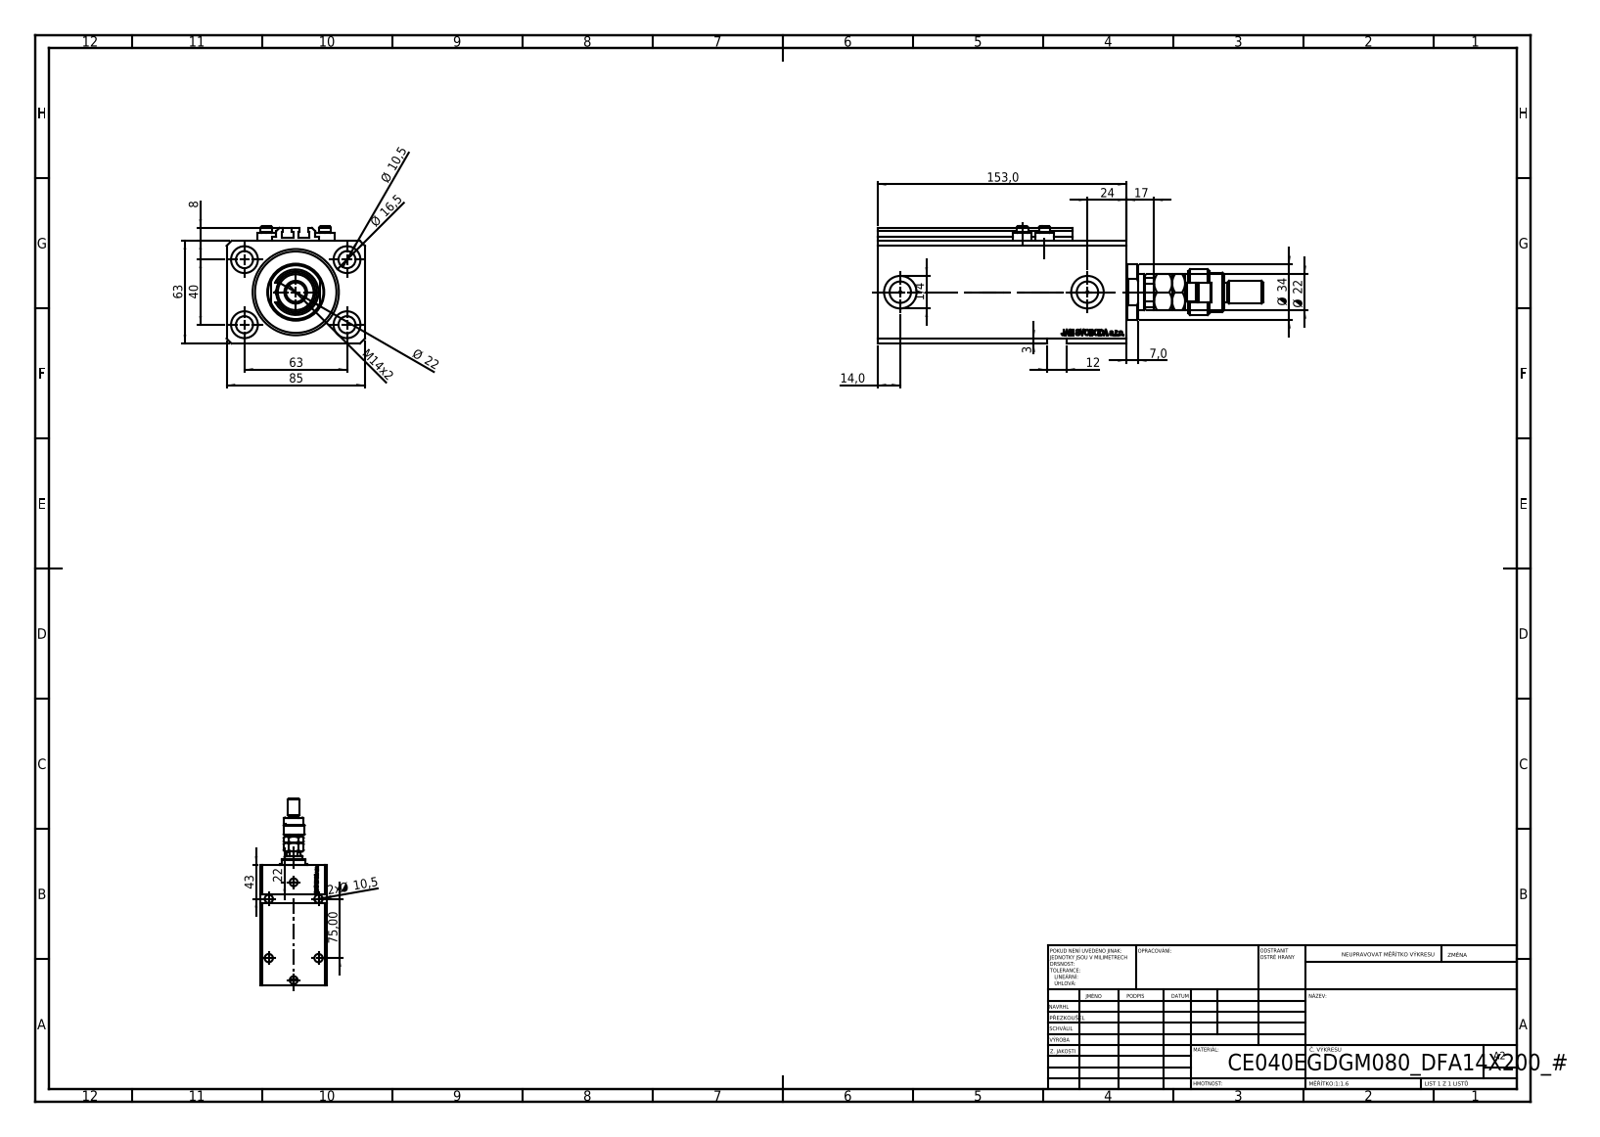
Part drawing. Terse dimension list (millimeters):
name: ALLEN BOLT V250CE; V250CE_E_Body; FEMALE_PART_FOR_DFA; V250CE_C_VCP (+2 more)
written by: SolidWorks 2019 (CONFIG_CONTROL_DESIGN)
unit: mm
bodies: 10 solids, 1208 faces (567 planar, 171 cylindrical, 470 other)
size: 237 × 85 × 72
volume: 702 141 mm³; area: 149 940 mm²
holes: 8× ⌀10.5, 4× ⌀1.25, 4× ⌀4, 4× ⌀16.5, 2× ⌀10, 2× ⌀13.16, 2× ⌀20, 1× ⌀12.5, 1× ⌀22, 1× ⌀40, 1× ⌀53
bosses: 4× ⌀11.6, 4× ⌀7, 1× ⌀34, 1× ⌀28, 1× ⌀24, 1× ⌀18, 1× ⌀14, 1× ⌀12
rounds: 10× R0.2, 1× R9.75, 1× R10.5
face distances: 63, 85, 17, 153, 136, 11.4, 124.6, 141.6, 3, 65
hole spacings: 37.31, 63, 13.6, 15.4, 24.96, 33.62, 36, 37.86
